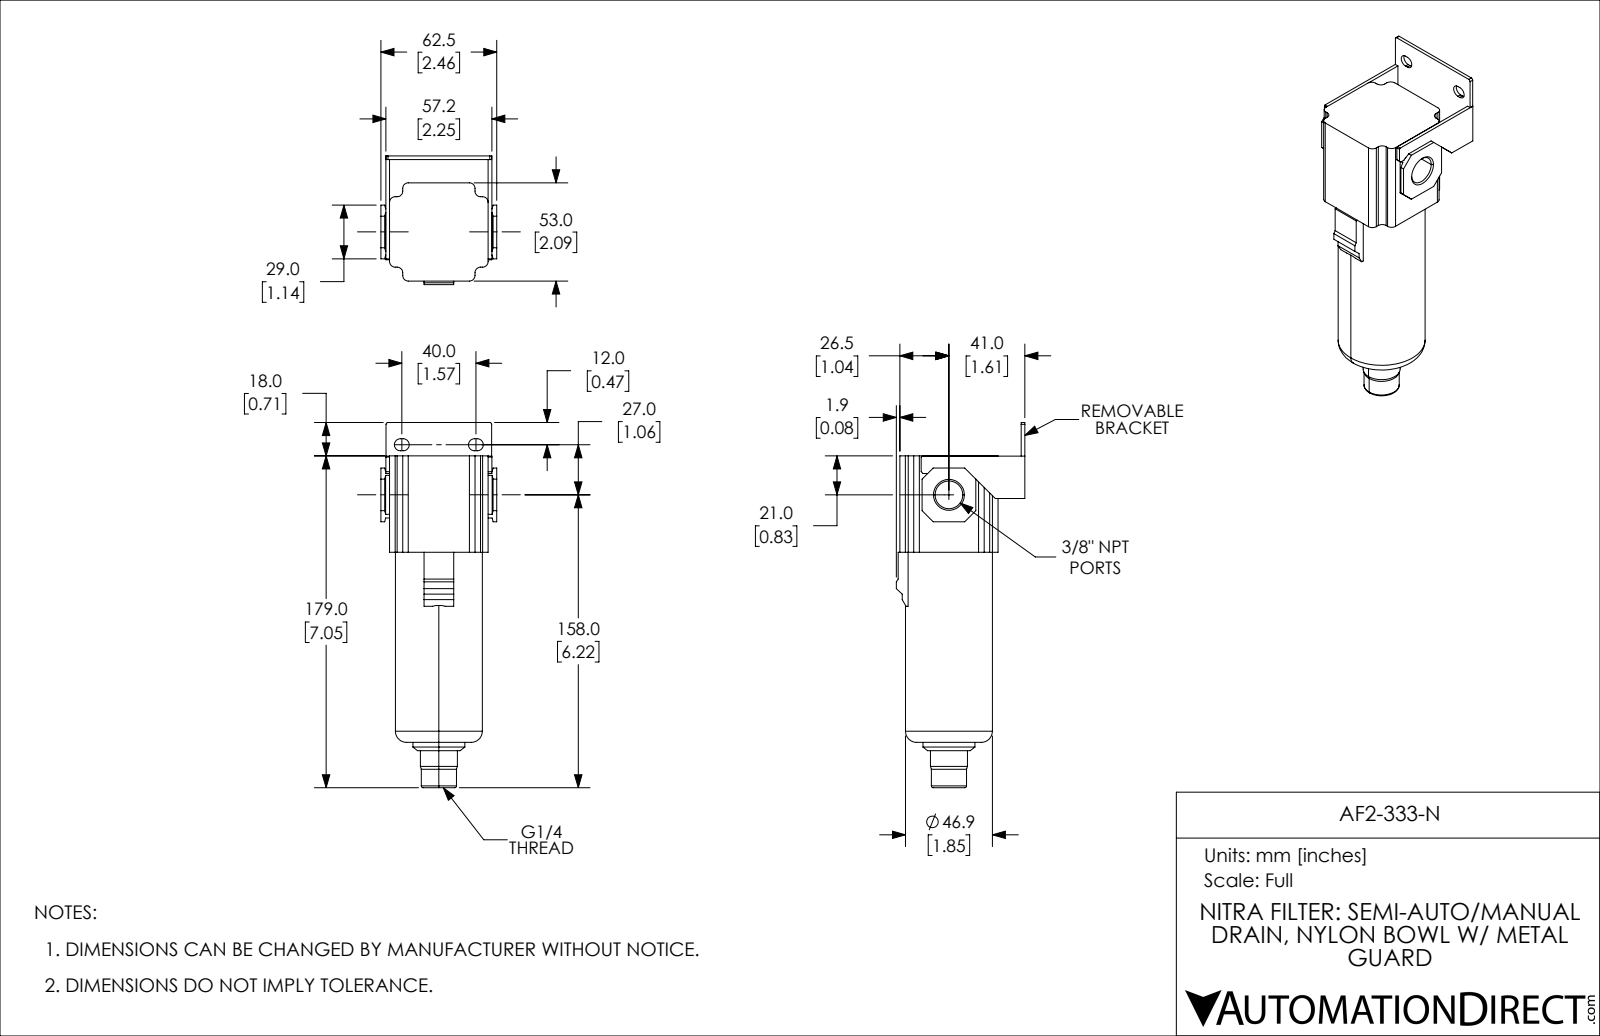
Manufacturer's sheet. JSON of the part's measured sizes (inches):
{"part_name": "AF2-333-N", "step_written_by": "SolidWorks 2019 (CONFIG_CONTROL_DESIGN)", "units": "inches", "bodies": {"solids": 1, "faces": 137, "planar": 91, "cylindrical": 32, "other": 14}, "overall_size": [7.756, 2.733, 2.461], "volume_in3": 20.09, "surface_area_in2": 65.35, "round_holes": [[0.337, 1], [0.589, 1]], "round_bosses_or_shafts": [[1.846, 1], [1.102, 1], [0.787, 1], [0.748, 1]], "partial_cylinders_radius": [[0.118, 12], [0.128, 4], [0.039, 2]], "face_to_face_distances": [0.079, 0.492, 0.571, 2.657, 2.579, 2.087, 2.173, 2.094, 0.104, 0.183]}
